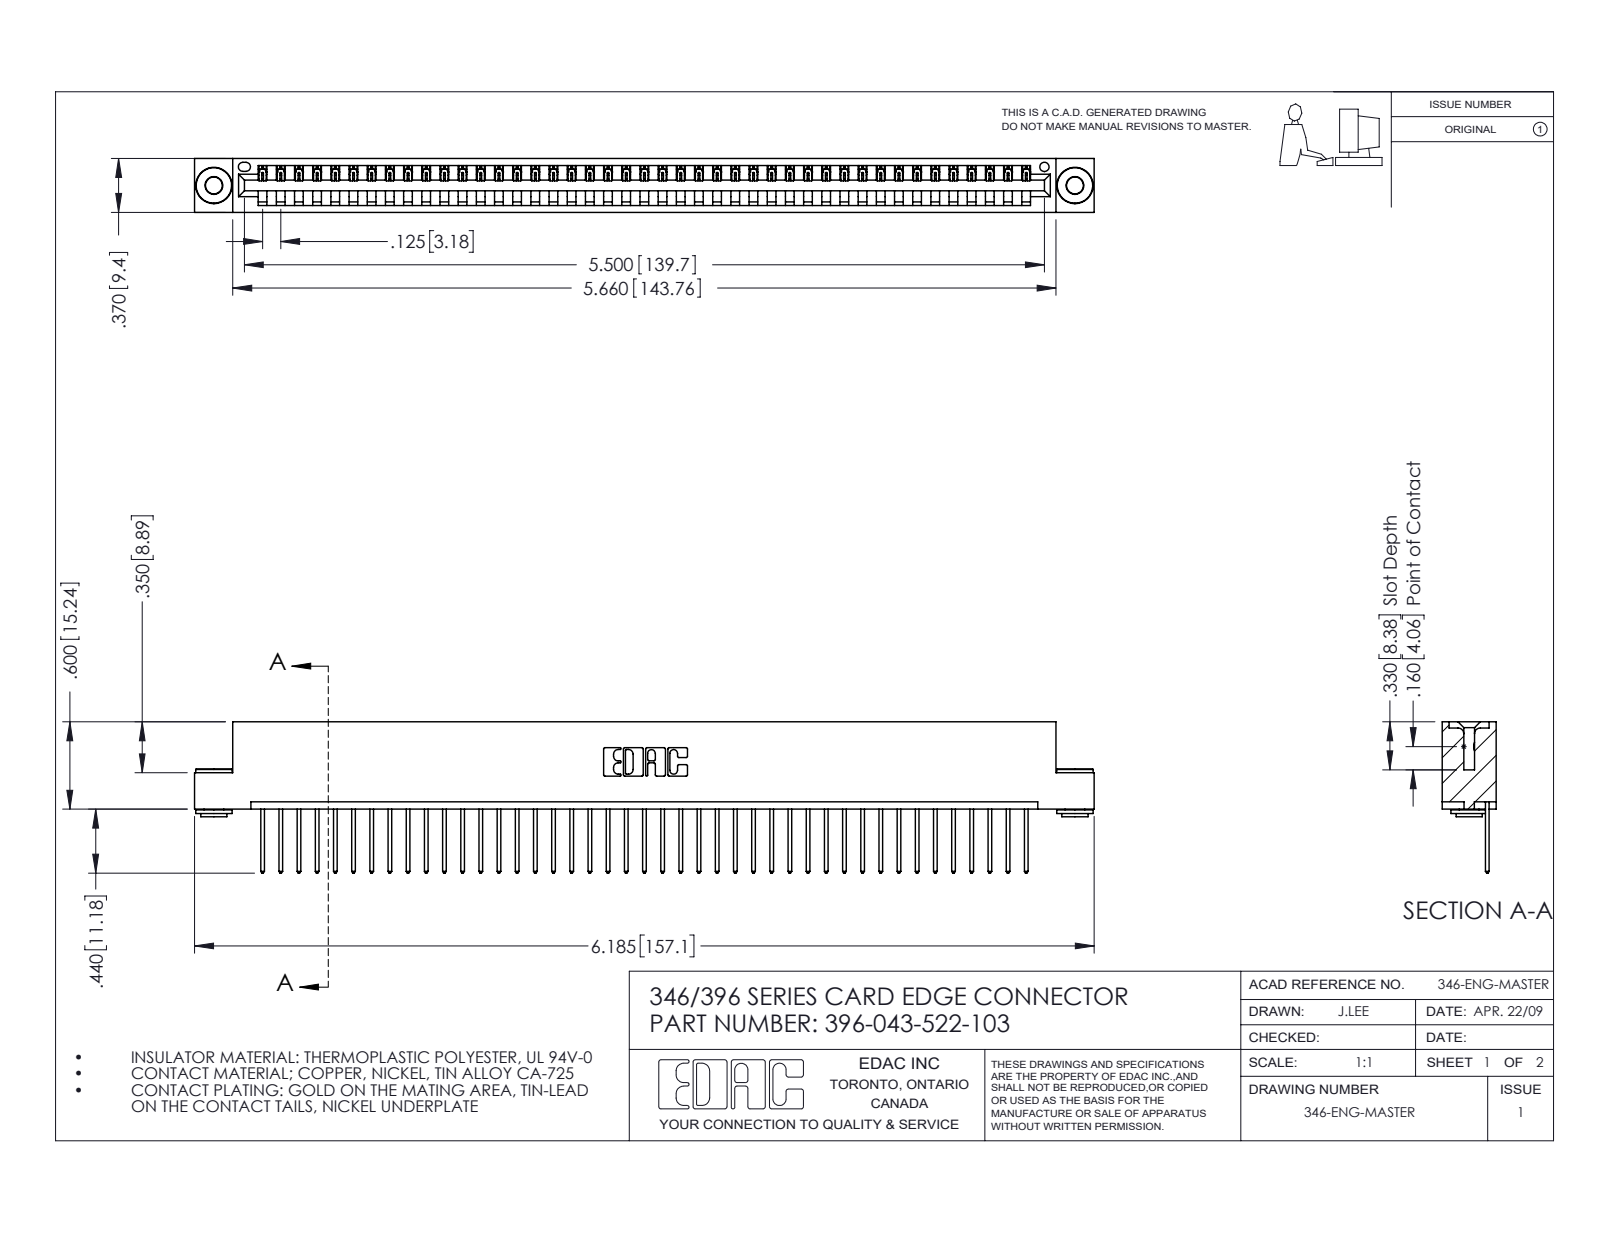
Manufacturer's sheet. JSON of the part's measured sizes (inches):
{"part_name": "396-043-522-103; 345-292-001_345-293-122; 346 Part_Flush Mounting Lugs - 0.156 Dia-TH; 345-250-002_345-250-002-102", "step_written_by": "SolidWorks 2016 (CONFIG_CONTROL_DESIGN)", "units": "inches", "bodies": {"solids": 46, "faces": 2654, "planar": 1806, "cylindrical": 840, "other": 8}, "overall_size": [6.185, 1.04, 0.37], "volume_in3": 0.92, "surface_area_in2": 29.8, "round_holes": [[0.116, 2], [0.156, 2], [0.064, 1]], "round_bosses_or_shafts": [[0.25, 2], [0.18, 2], [0.136, 2]], "partial_cylinders_radius": [[0.006, 86], [0.01, 86], [0.01, 22], [0.007, 6], [0.031, 6], [0.026, 3], [0.031, 2], [0.04, 2]], "face_to_face_distances": [0.048, 0.322, 0.37, 0.25, 0.025, 0.072, 0.298, 0.148, 0.222, 0.1], "hole_center_spacings": [0.246, 5.711, 5.92]}
